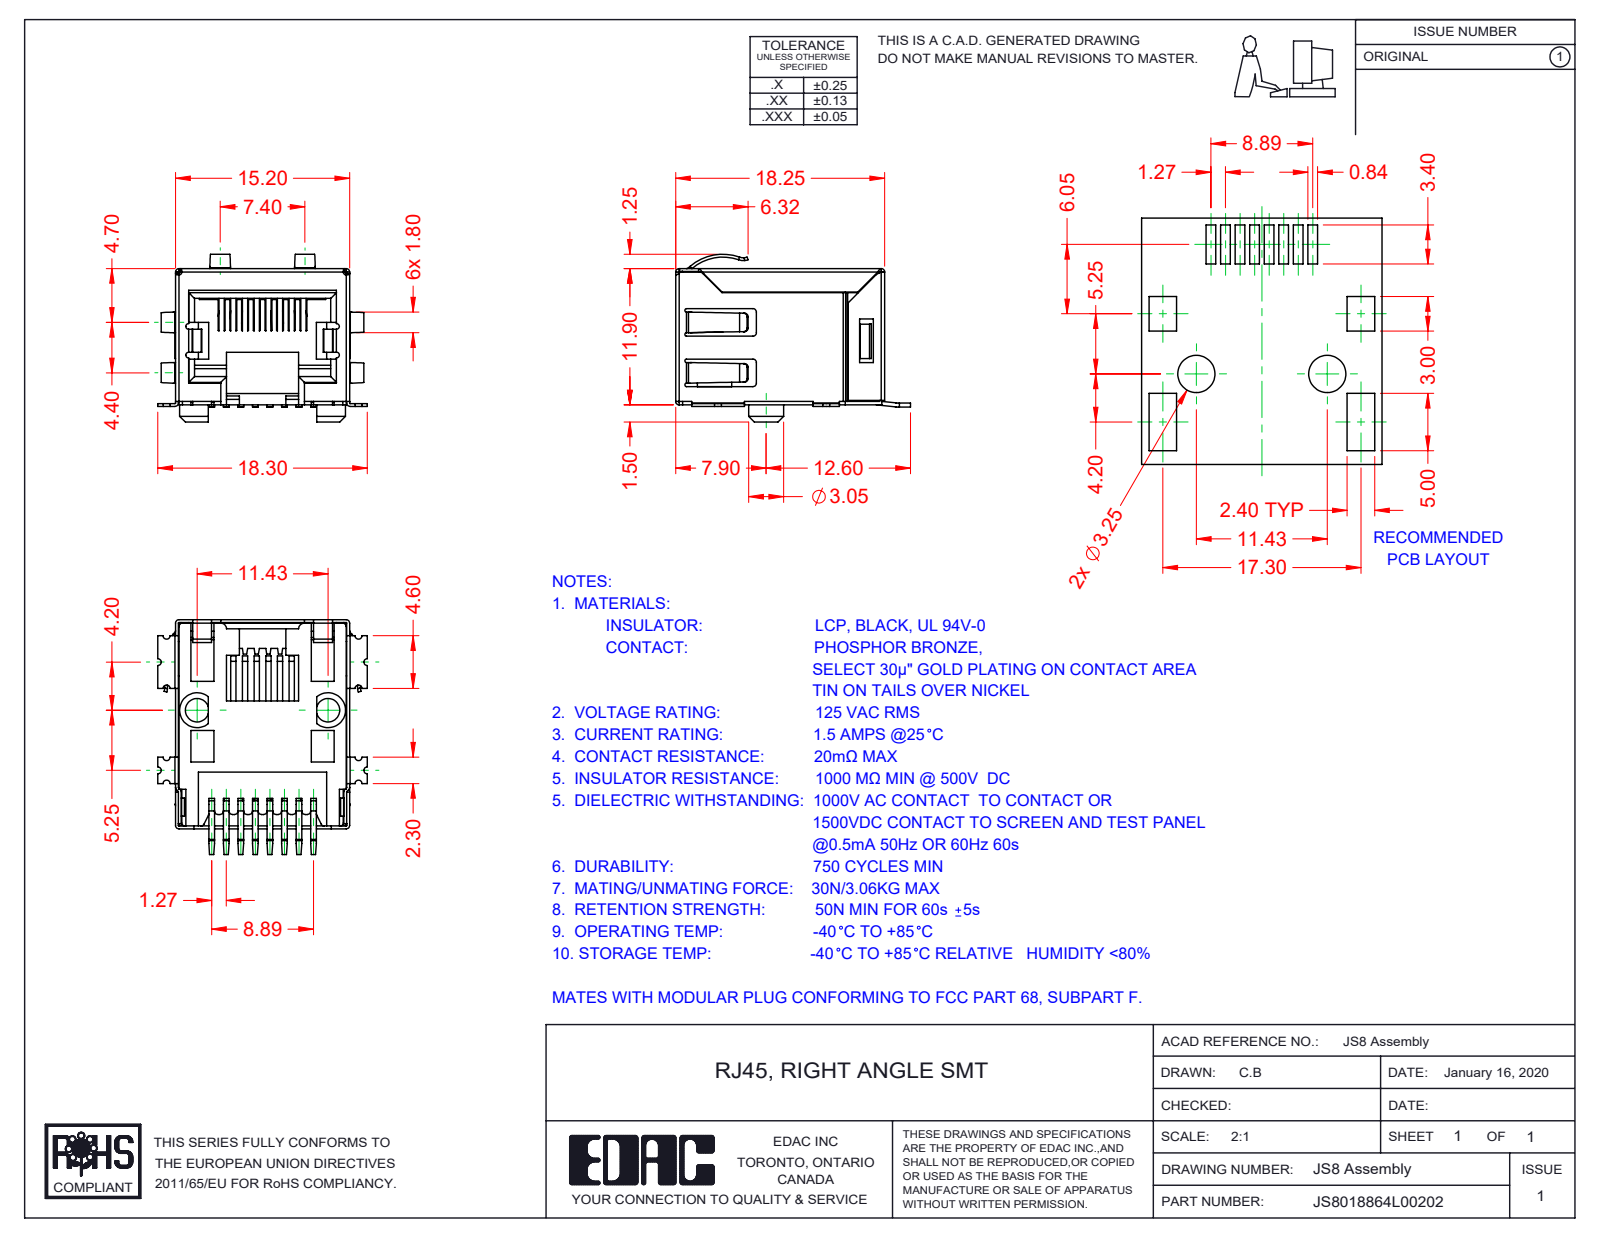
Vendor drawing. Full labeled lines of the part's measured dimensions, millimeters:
Part name (STEP PRODUCT): S8 Shield; S8 Contacts; RJS8018864L00202; S8 Insulator
STEP written by: SolidWorks 2016 (CONFIG_CONTROL_DESIGN)
Units: millimetres
Bodies: 10 solids, 976 faces (602 planar, 314 cylindrical, 60 other)
Overall size (bounding box): 20.5 × 18.3 × 14.65
Volume: 1 308 mm³ · Surface area: 4 634 mm²
Partial cylindrical surfaces — rounded edges, fillets, slot ends (radius × count): R0.3 ×59, R0.25 ×19, R0.5 ×18, R0.2 ×17, R0.15 ×8, R0.75 ×7, R1 ×4, R1.25 ×3
Main face-to-face distances: 14.65, 14.95, 14.9, 1, 0.35, 14.7, 0.75, 10.9, 1.1, 15.2
